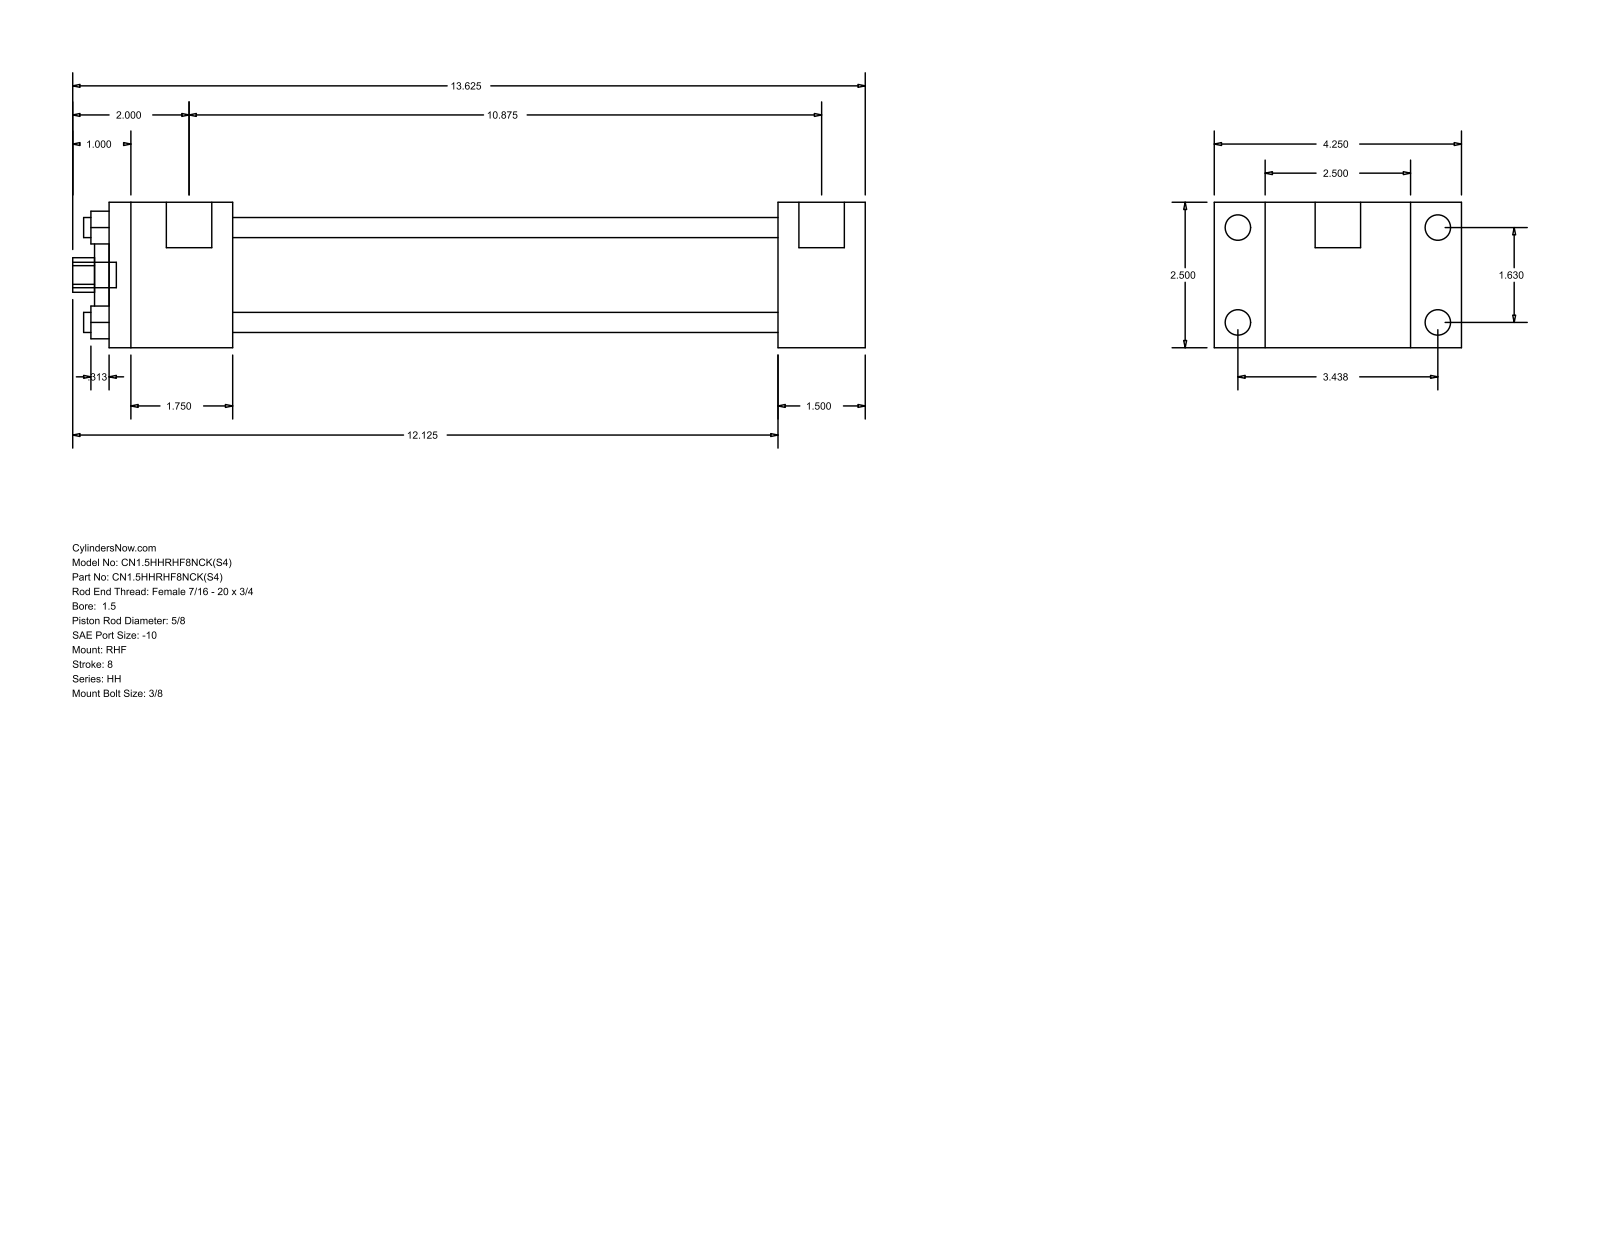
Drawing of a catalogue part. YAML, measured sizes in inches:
part_name: "HH_RHF__0150_0.625"
step_written_by: "GSSL Pune (CONFIG_CONTROL_DESIGN)"
units: inches
bodies: {solids: 0, faces: 88, planar: 60, cylindrical: 28, other: 0}
overall_size: [13.625, 4.25, 2.5]
round_holes:
  - {diameter: 0.345, count: 4}
  - {diameter: 0.625, count: 1}
  - {diameter: 1.125, count: 1}
  - {diameter: 1.75, count: 1}
round_bosses_or_shafts:
  - {diameter: 0.438, count: 4}
  - {diameter: 0.219, count: 4}
  - {diameter: 0.781, count: 2}
  - {diameter: 0.437, count: 1}
partial_cylinders:
  - {radius: 0.297, count: 1}
face_to_face_distances: [2.5, 0.875, 3.375, 1.5, 11.5, 13, 4.25, 2.125, 9.375, 10.875]
hole_center_spacings: [1.152, 1.63, 2.305]
